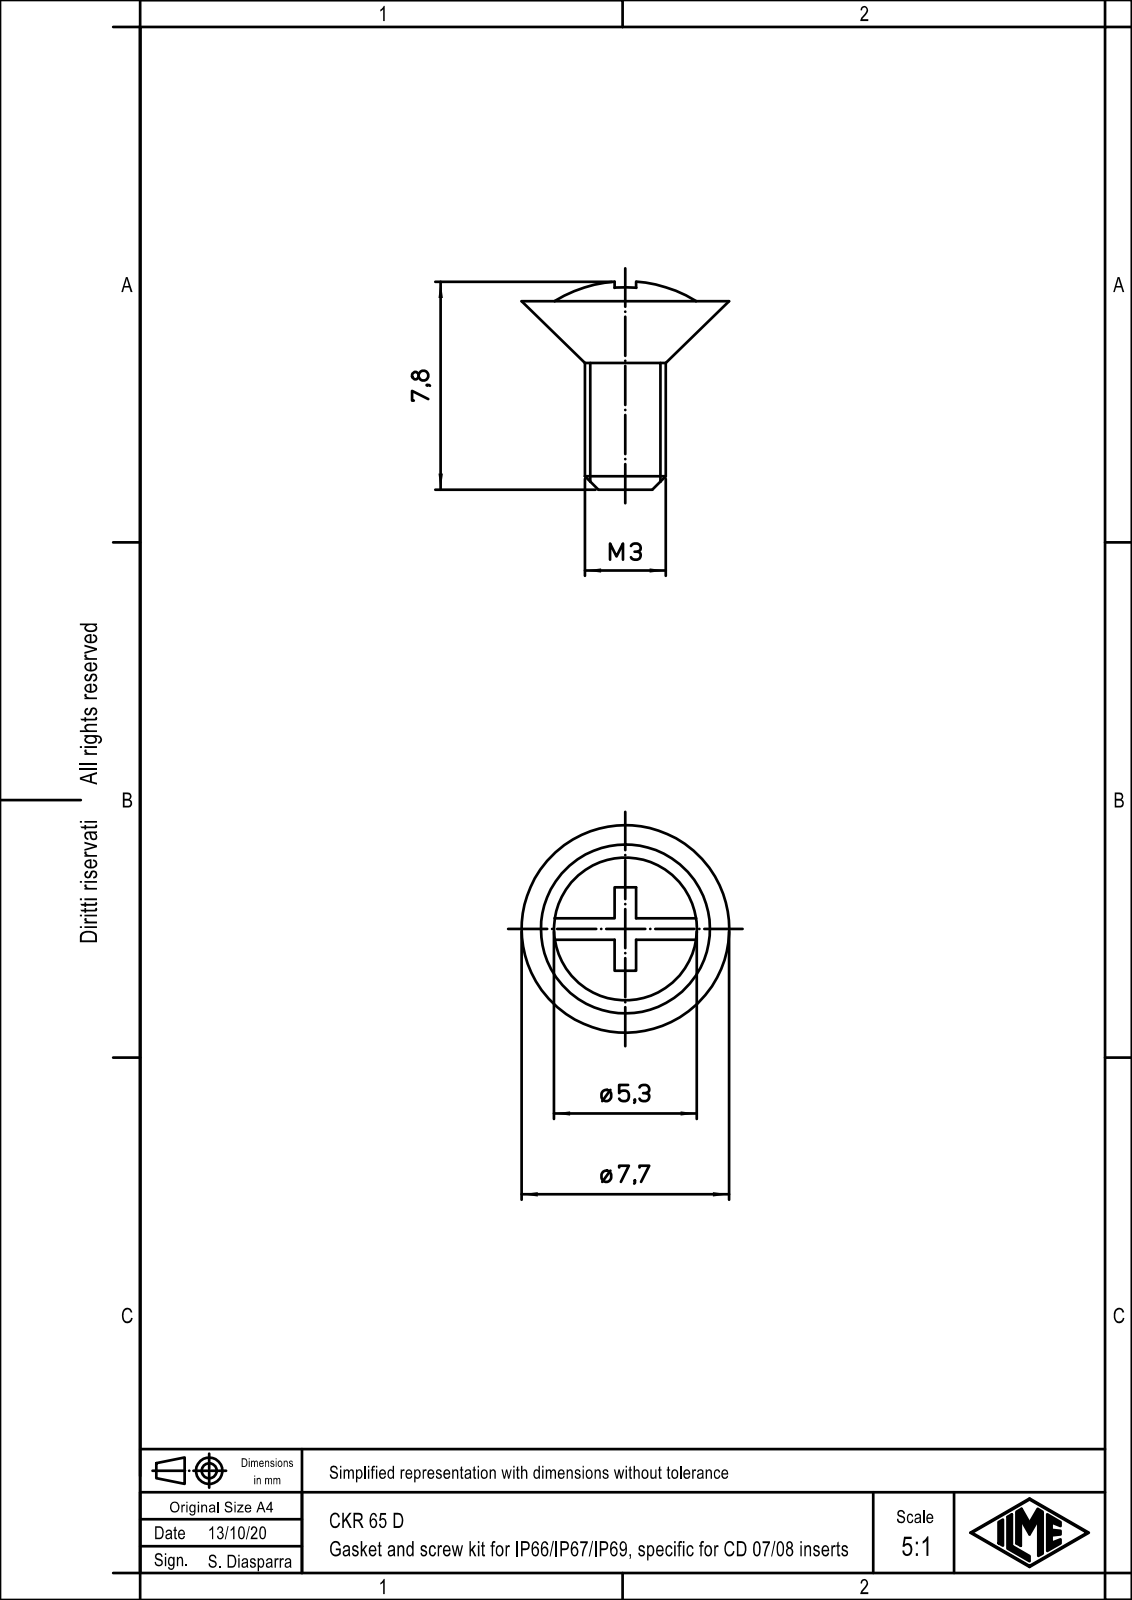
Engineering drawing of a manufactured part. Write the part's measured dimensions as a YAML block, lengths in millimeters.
part_name: "CKR_65_D"
step_written_by: "OneSpace Modeling 15.50B 03-Nov-2007 (C) CoCreate Software GmbH (AUTOMOTIVE_DESIGN)"
units: millimeters
bodies: {solids: 1, faces: 72, planar: 26, cylindrical: 4, other: 42}
overall_size: [7.7, 7.7, 7.69]
volume: 86
surface_area: 192
round_bosses_or_shafts:
  - {diameter: 5.6, count: 1}
  - {diameter: 3.2, count: 1}
face_to_face_distances: [7, 6.23, 0.77, 1.38, 0.8, 4.05, 2.18, 2.95, 6.83, 2.78]
